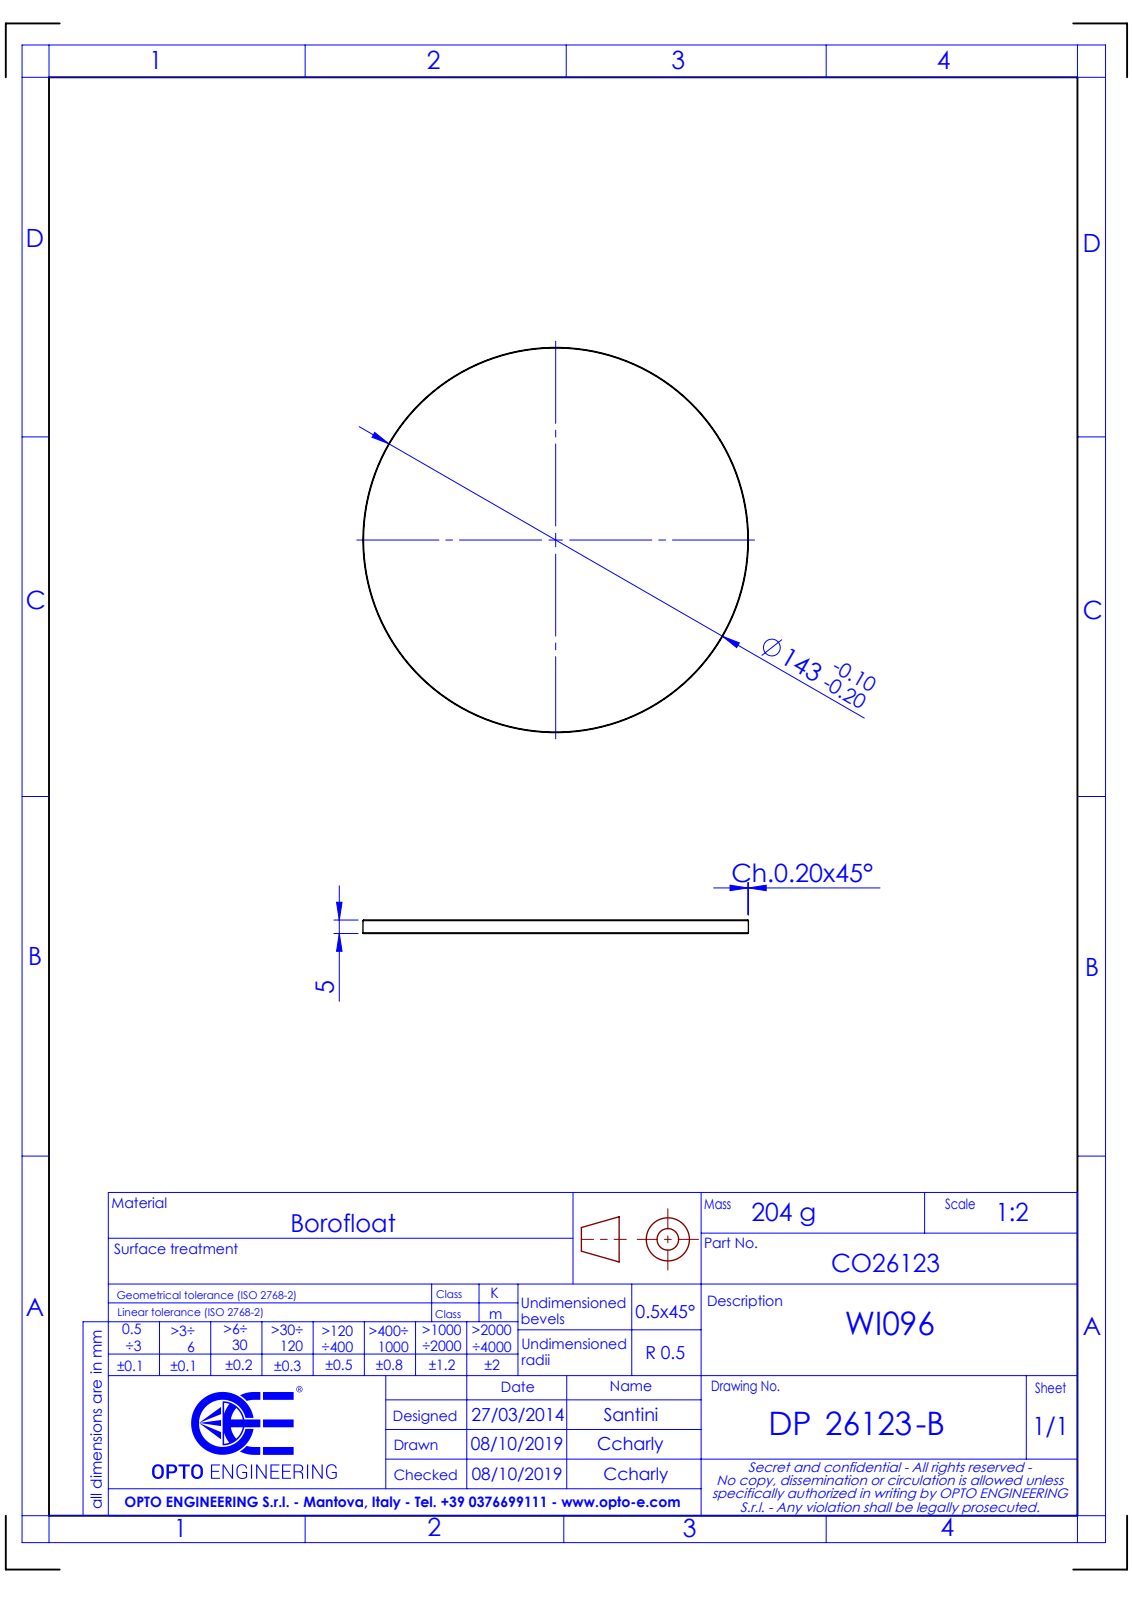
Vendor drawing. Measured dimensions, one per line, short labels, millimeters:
name: DP26123_WI096
written by: SolidWorks 2021 (CONFIG_CONTROL_DESIGN)
unit: mm
bodies: 1 solid, 8 faces (2 planar, 2 cylindrical, 4 other)
size: 143 × 143 × 5
volume: 80 285 mm³; area: 34 262 mm²
bosses: 1× ⌀143
face distances: 5
